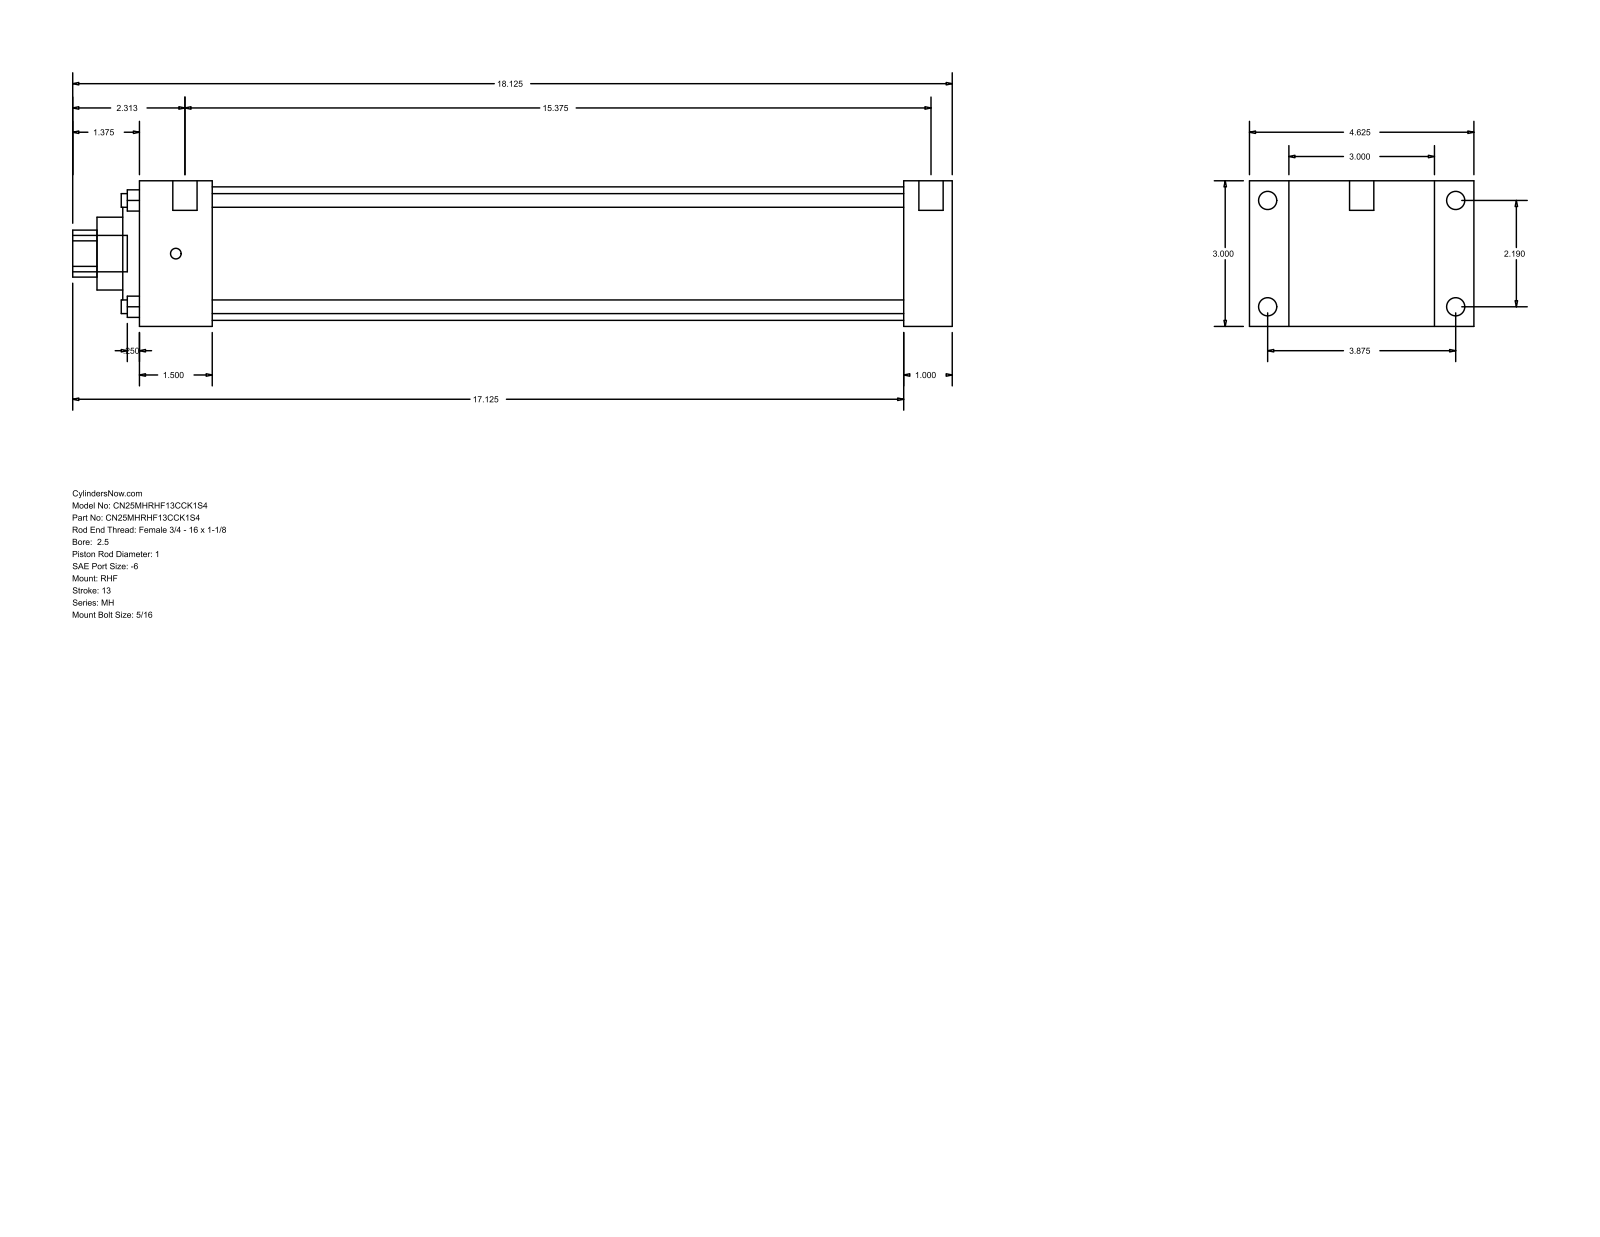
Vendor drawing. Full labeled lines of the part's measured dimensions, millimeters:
Part name (STEP PRODUCT): MH_RHF__0250_1
STEP written by: GSSL Pune (CONFIG_CONTROL_DESIGN)
Units: millimetres
Bodies: 0 solids, 90 faces (61 planar, 29 cylindrical, 0 other)
Overall size (bounding box): 460.38 × 117.47 × 76.2
Round holes (diameter × count): ⌀7.14 ×4, ⌀25.4 ×1, ⌀38.1 ×1, ⌀60.33 ×1, ⌀69.85 ×1
Round bosses / shafts (diameter × count): ⌀9.53 ×4, ⌀5.56 ×4, ⌀12.7 ×2, ⌀19.05 ×1
Partial cylindrical surfaces — rounded edges, fillets, slot ends (radius × count): R12.29 ×1
Main face-to-face distances: 76.2, 25.4, 20.64, 96.84, 400.06, 425.46, 117.48, 38.11, 361.95, 387.35
Hole centre spacings: 39.33, 55.62, 78.66
